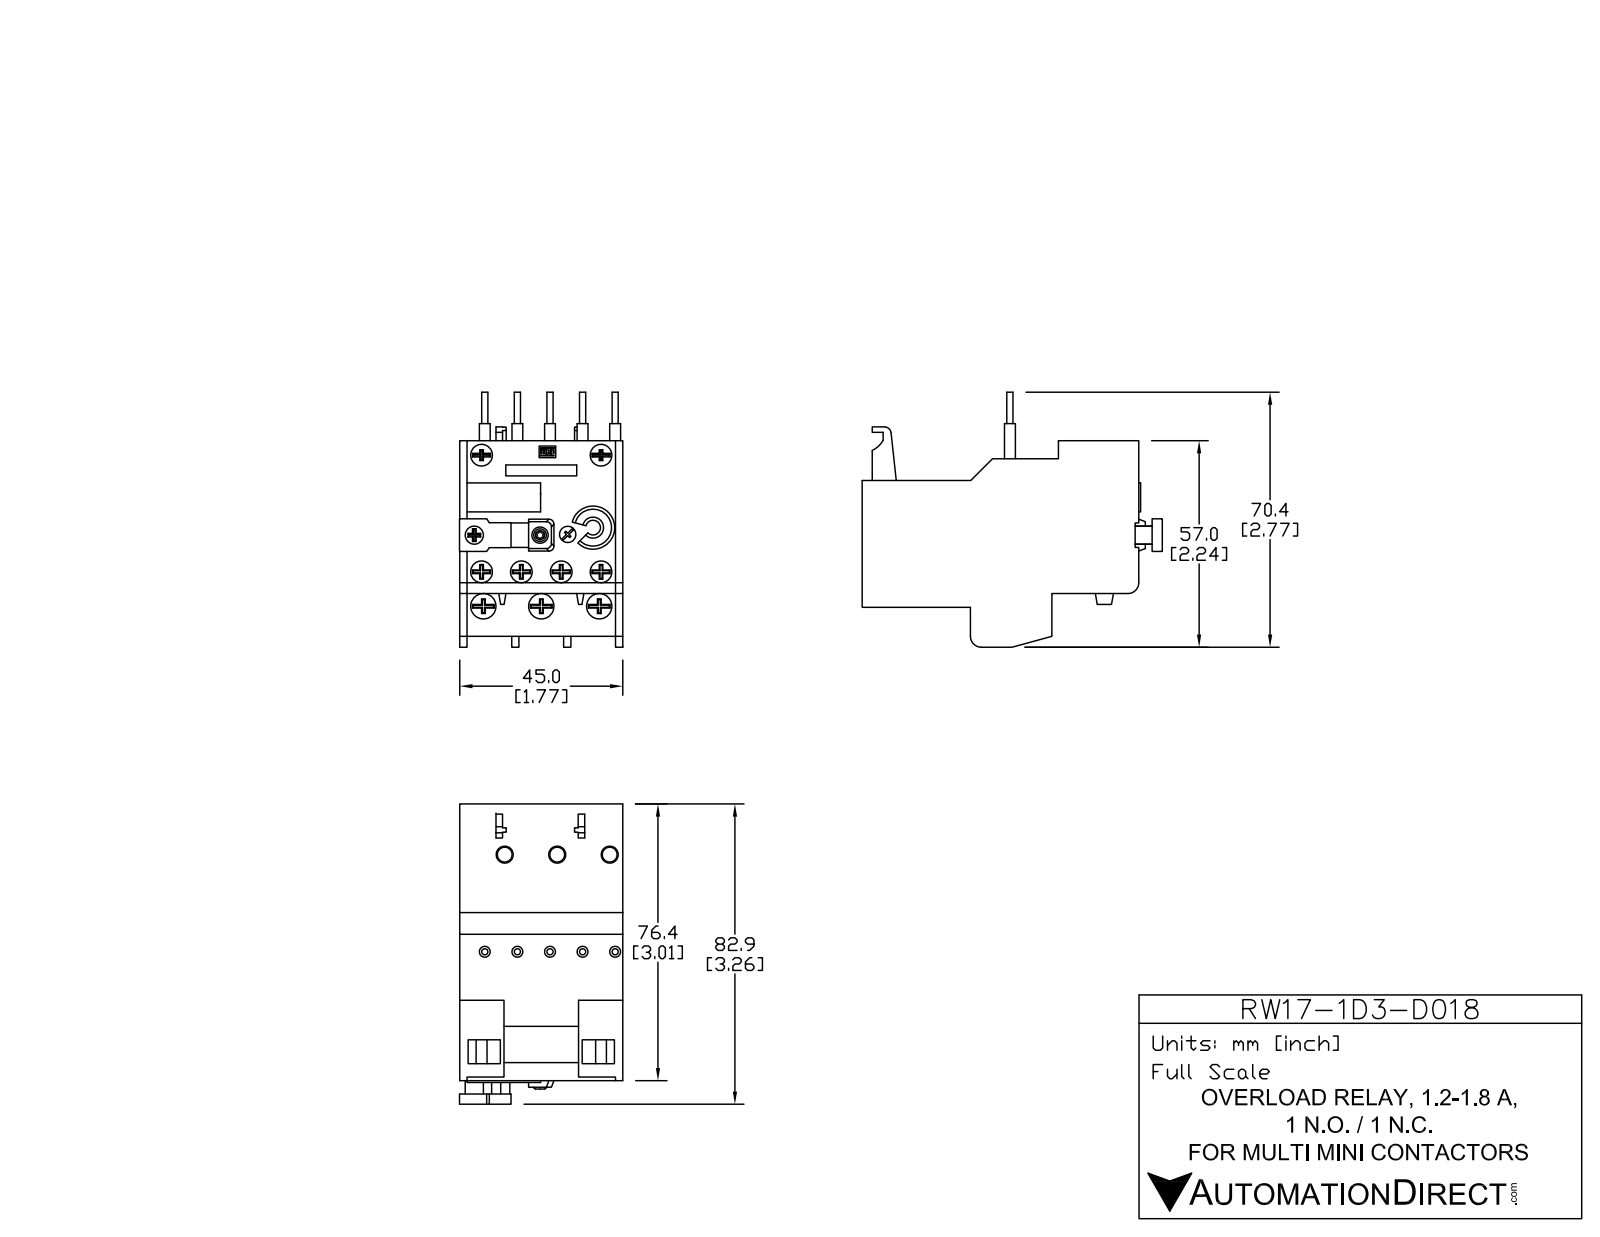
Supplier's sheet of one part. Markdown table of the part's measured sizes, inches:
| quantity | value |
| --- | --- |
| part name | RW17D-1D3-D018 |
| STEP written by | SolidWorks 2013 (AUTOMOTIVE_DESIGN) |
| units | inches |
| bodies | 18 solids, 756 faces (515 planar, 214 cylindrical, 27 other) |
| overall size | 3.254 × 2.776 × 1.793 |
| volume | 7.778 in³ |
| surface area | 53.79 in² |
| round holes (diameter × count) | 0.236 × 6, 0.157 × 3, 0.276 × 3, 0.295 × 3, 0.177 × 1, 0.187 × 1, 0.21 × 1, 0.217 × 1, 0.41 × 1 |
| round bosses / shafts (diameter × count) | 0.217 × 7, 0.118 × 7, 0.069 × 5, 0.22 × 2, 0.128 × 2, 0.253 × 1, 0.242 × 1, 0.187 × 1 |
| partial cylindrical surfaces (radius × count) | 0.02 × 20, 0.01 × 12, 0.039 × 9, 0.178 × 6, 0.231 × 4, 0.309 × 4, 0.059 × 3, 0.049 × 2 |
| main face-to-face distances | 1.791, 0.059, 0.427, 0.433, 3.008, 1.378, 0.056, 2.952, 2.949, 0.236 |
| hole center spacings | 0.591, 0.337, 0.423, 1.181, 0.416, 0.467, 0.561, 0.841 |
